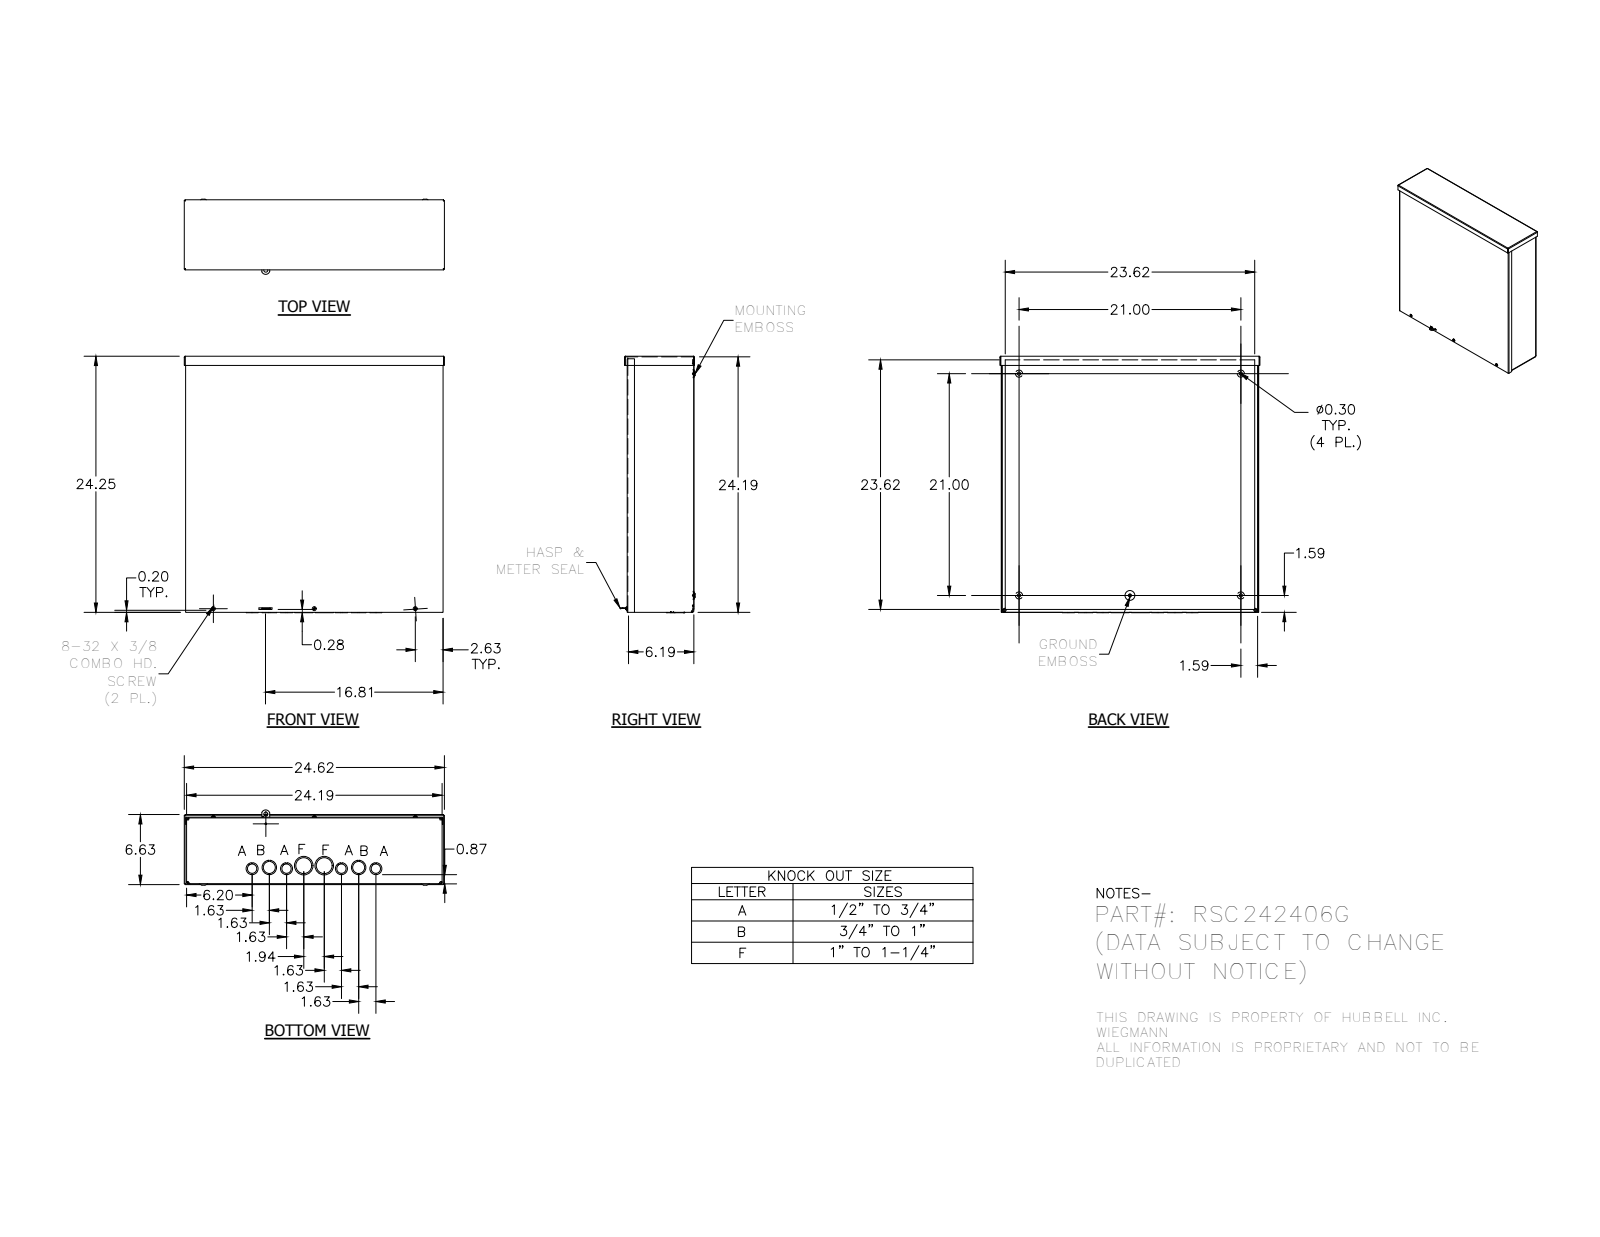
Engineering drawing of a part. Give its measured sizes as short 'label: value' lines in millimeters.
name: RSC242406G_WRAP; RSC2424G_LID; RSC2406G_CAP; 3183 (+4 more)
written by: Autodesk Inventor 2014 (AUTOMOTIVE_DESIGN)
unit: mm
bodies: 8 solids, 661 faces (322 planar, 176 cylindrical, 163 other)
size: 625.48 × 616.73 × 180.97
volume: 2 158 000 mm³; area: 2 757 000 mm²
holes: 6× ⌀7.95, 6× ⌀28.57, 4× ⌀7.62, 4× ⌀22.22, 3× ⌀3.76, 2× ⌀3.17, 2× ⌀34.92, 2× ⌀38.1, 2× ⌀44.45, 1× ⌀3.96, 1× ⌀4.19, 1× ⌀9.52
bosses: 3× ⌀9.75, 3× ⌀4.17, 1× ⌀5.8
rounds: 16× R0.25, 8× R0.79, 8× R2.37, 8× R3.17, 8× R4.75, 6× R0.79, 5× R0.63, 4× R1.4
face distances: 1.58, 158.73, 157.15, 1.59, 612.79, 160.32, 158.74, 1.57, 614.37, 3.15
hole spacings: 41.52, 533.4, 592.13, 640.01, 214.88, 42.07, 82.8, 82.91
